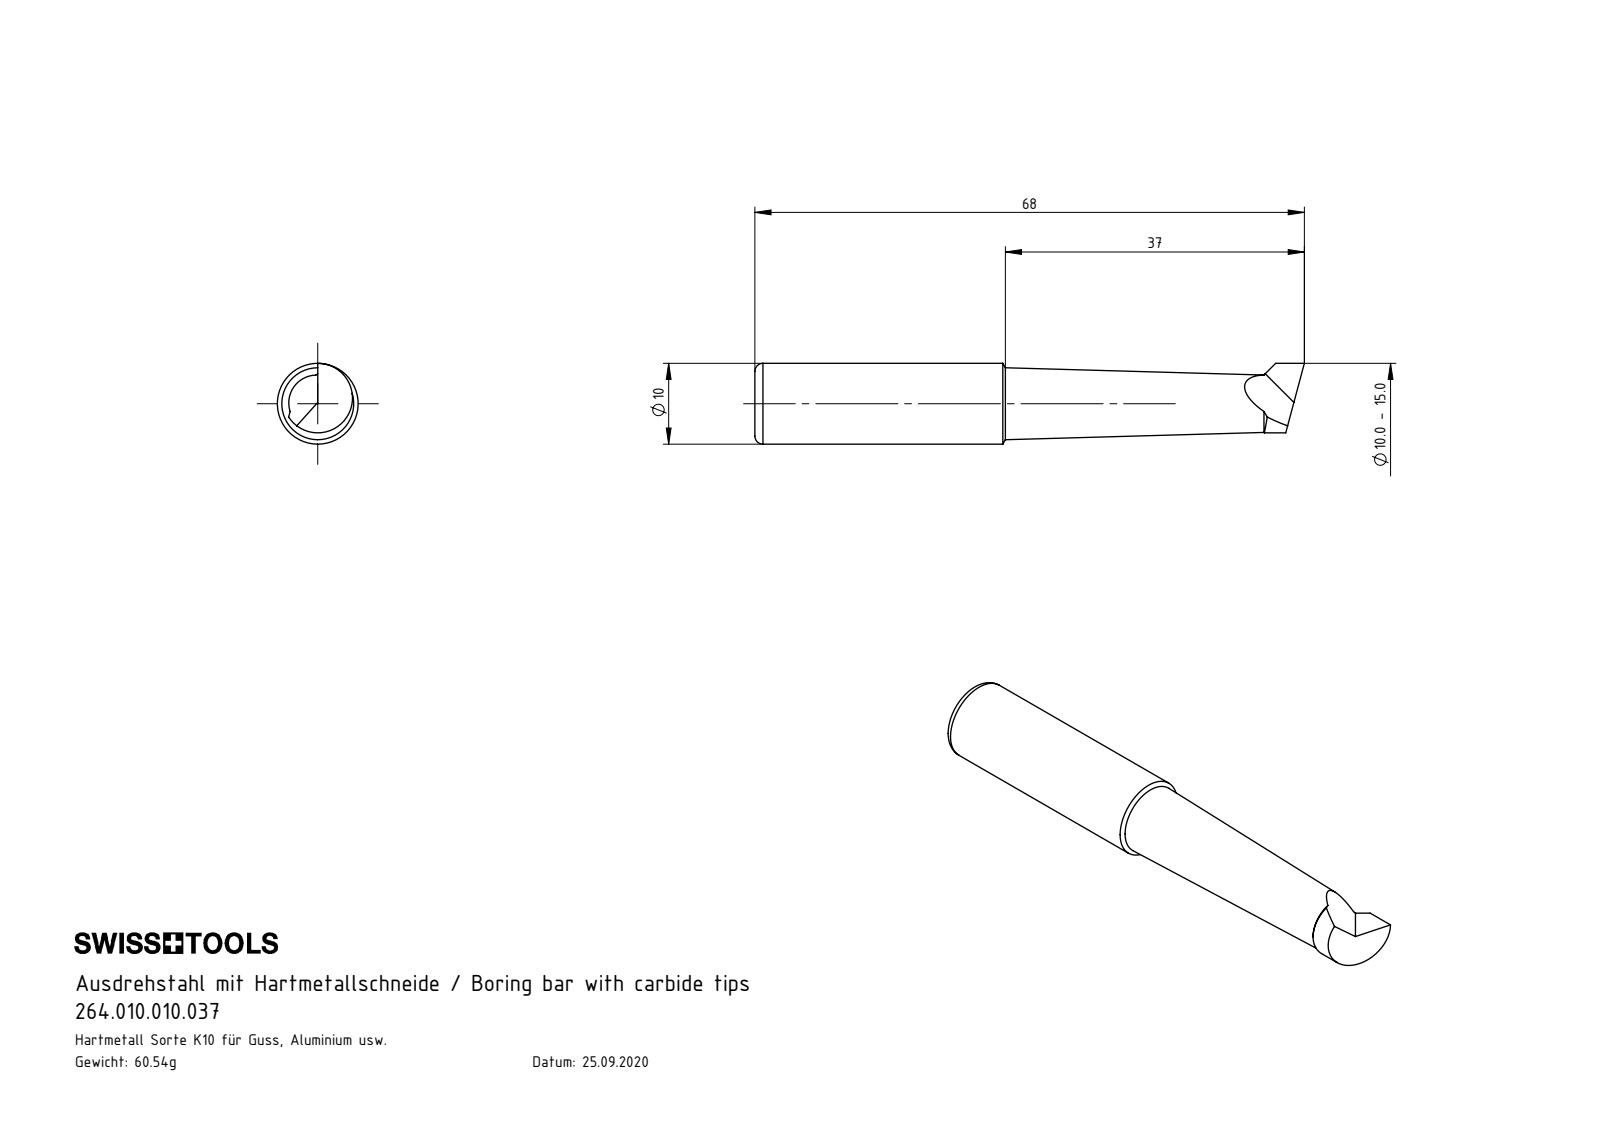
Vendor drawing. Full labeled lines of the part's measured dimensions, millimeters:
Part name (STEP PRODUCT): U10.B10.001.037
STEP written by: SolidWorks 2017 (AUTOMOTIVE_DESIGN)
Units: millimetres
Bodies: 1 solid, 10 faces (4 planar, 2 cylindrical, 4 other)
Overall size (bounding box): 68 × 10 × 10
Volume: 4 175 mm³ · Surface area: 1 987 mm²
Round bosses / shafts (diameter × count): ⌀10 ×1
Partial cylindrical surfaces — rounded edges, fillets, slot ends (radius × count): R4.3 ×1
